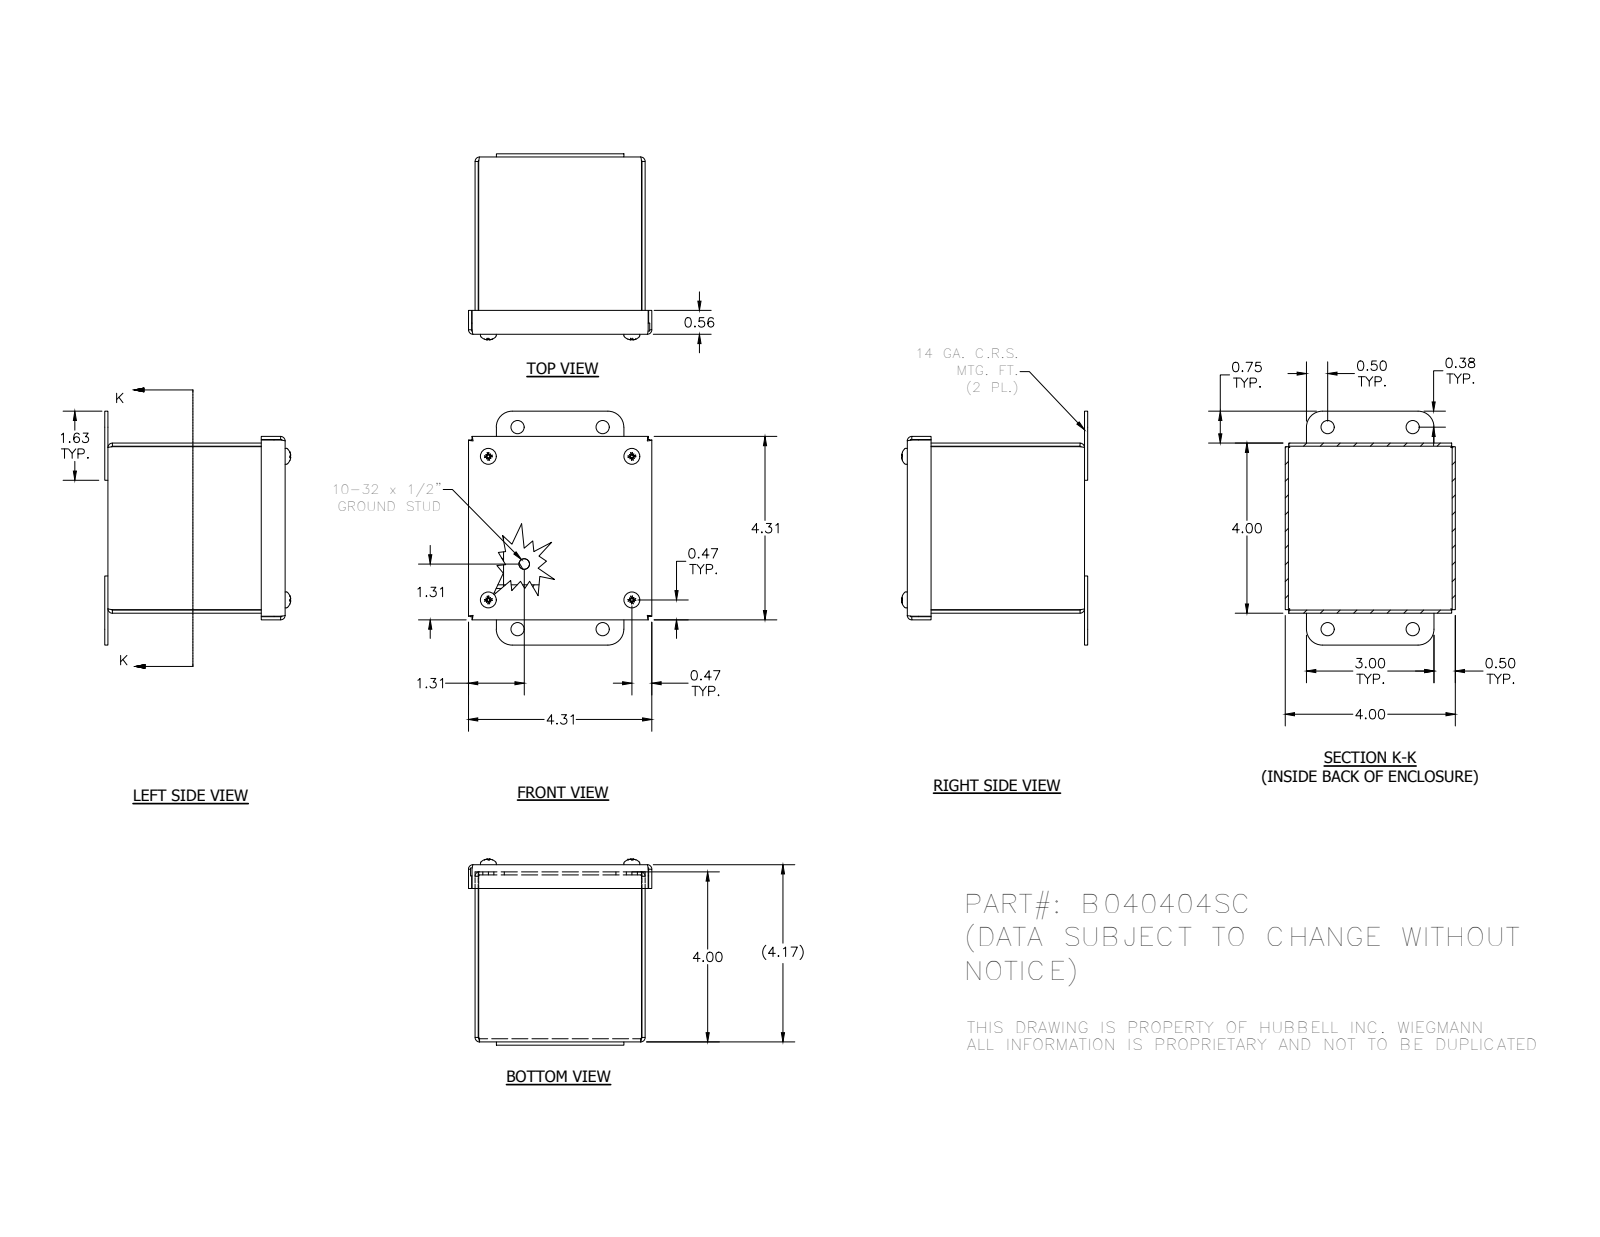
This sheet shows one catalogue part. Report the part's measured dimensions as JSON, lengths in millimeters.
{"part_name": "B040404SC; 3481; 34984; B040404SCBKP (+5 more)", "step_written_by": "Autodesk Inventor 2012 (AUTOMOTIVE_DESIGN)", "units": "millimeters", "bodies": {"solids": 19, "faces": 496, "planar": 299, "cylindrical": 90, "other": 107}, "overall_size": [139.7, 110.4, 109.6], "volume_mm3": 173700, "surface_area_mm2": 175400, "round_holes": [[3.7, 4], [5, 4], [7.1, 4], [7.1, 4], [7.9, 4], [8, 4]], "round_bosses_or_shafts": [[4.8, 5], [11.5, 4], [10.3, 4], [9.5, 4], [6.3, 4], [6.4, 1]], "partial_cylinders_radius": [[0.8, 12], [2.7, 12], [2.3, 4], [9.5, 4]], "face_to_face_distances": [1.9, 99.7, 104, 101.6, 97.8, 105.9, 102.1, 99.2, 97.3, 4.8], "hole_center_spacings": [85.7, 85.7, 70.5, 85.4, 24.7, 0.4, 85.4, 86]}
